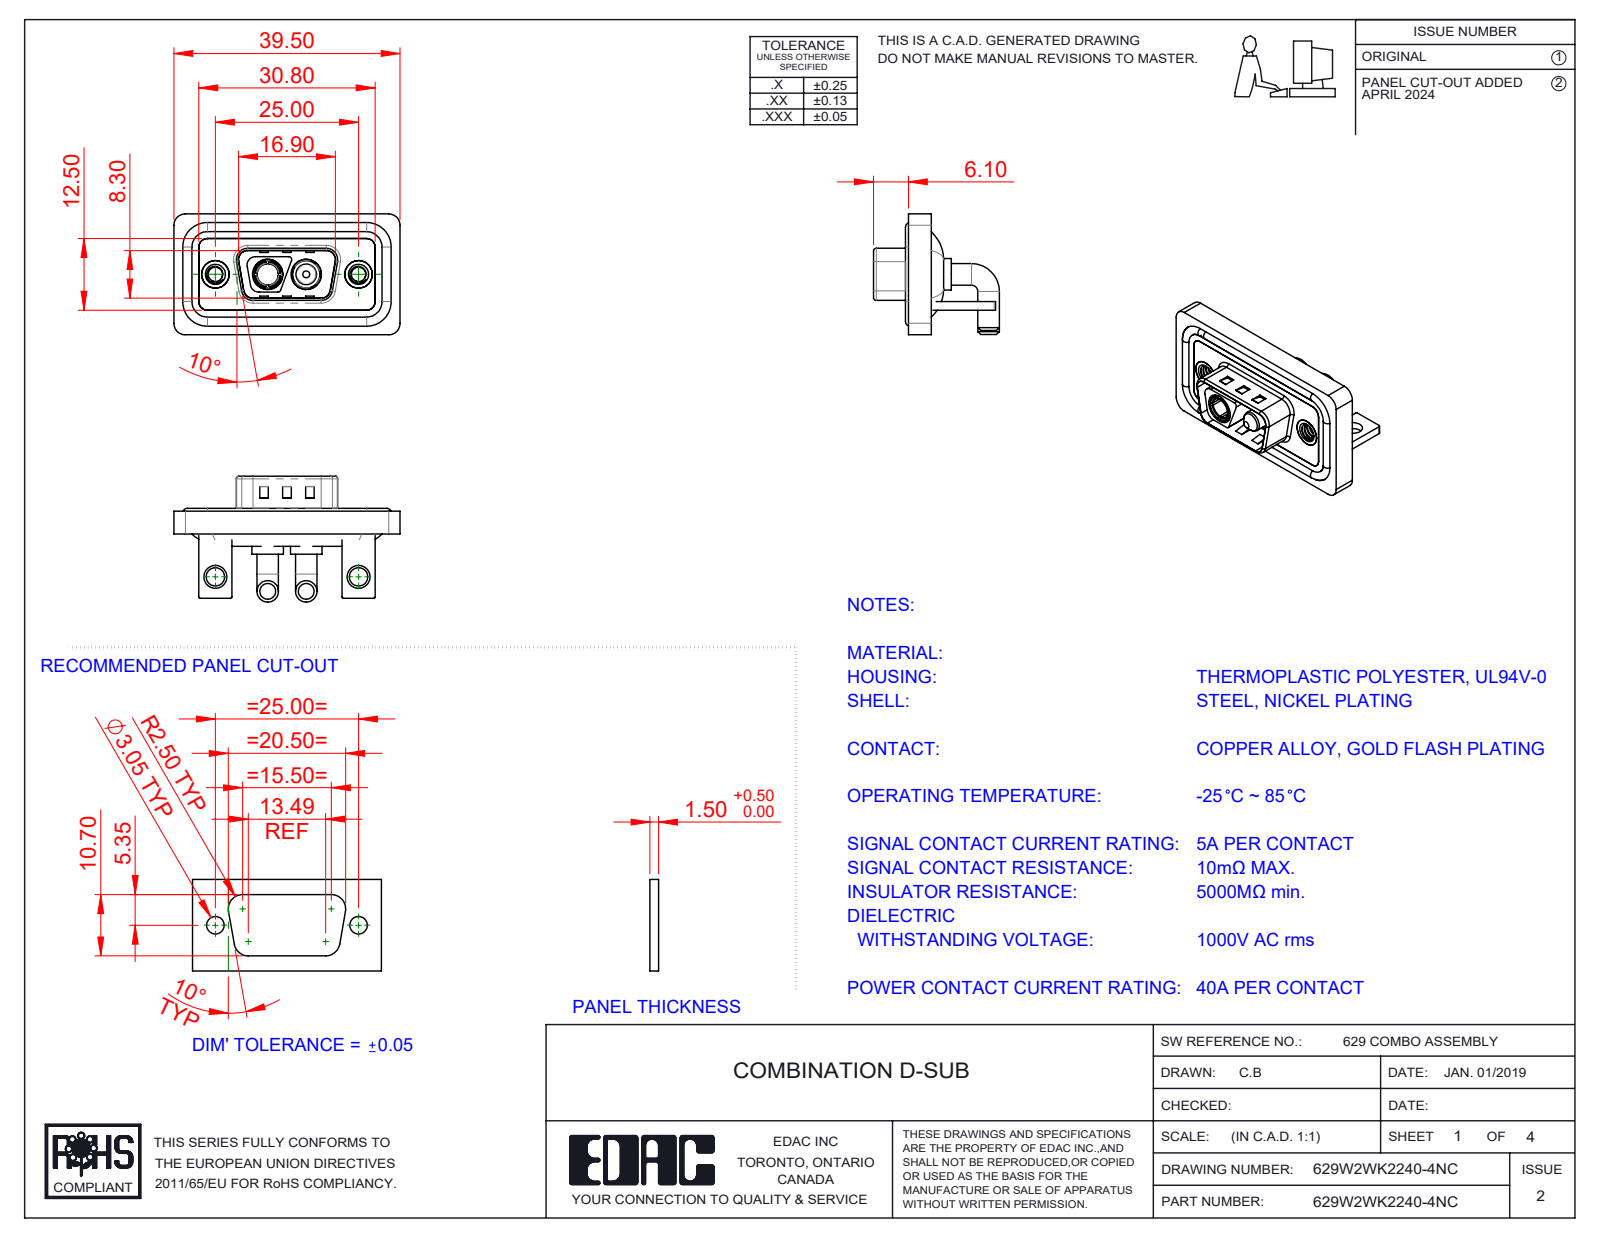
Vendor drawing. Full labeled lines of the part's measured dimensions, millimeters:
Part name (STEP PRODUCT): 629Combo Threaded Rivet_B; 629Combo Shell Front_09 Contacts; 629Combo Waterproof Housing_09 Contacts; 629Combo Stabilizer Bracket (+5 more)
STEP written by: SolidWorks 2023 (CONFIG_CONTROL_DESIGN)
Units: millimetres
Bodies: 13 solids, 580 faces (209 planar, 249 cylindrical, 122 other)
Overall size (bounding box): 39.5 × 21.98 × 21.1
Volume: 5 104 mm³ · Surface area: 8 210 mm²
Round holes (diameter × count): ⌀2.5 ×2, ⌀3.2 ×2, ⌀4 ×2, ⌀4.8 ×2, ⌀4.85 ×2, ⌀5 ×2, ⌀5.3 ×2, ⌀3.7 ×1
Round bosses / shafts (diameter × count): ⌀3.75 ×4, ⌀1.6 ×4, ⌀5.5 ×2, ⌀5.2 ×2, ⌀4.9 ×2, ⌀4.75 ×2, ⌀4.96 ×1, ⌀3.6 ×1
Partial cylindrical surfaces — rounded edges, fillets, slot ends (radius × count): R1.5 ×20, R2 ×19, R0.25 ×16, R0.5 ×11, R1.6 ×8, R0.6 ×4, R0.65 ×4, R0.9 ×4
Main face-to-face distances: 0.4, 1.5, 2.9, 0.8, 1.1, 1.2, 2.1, 1.6, 3.7, 2.5
Hole centre spacings: 9.14, 15.86, 25, 6.72
